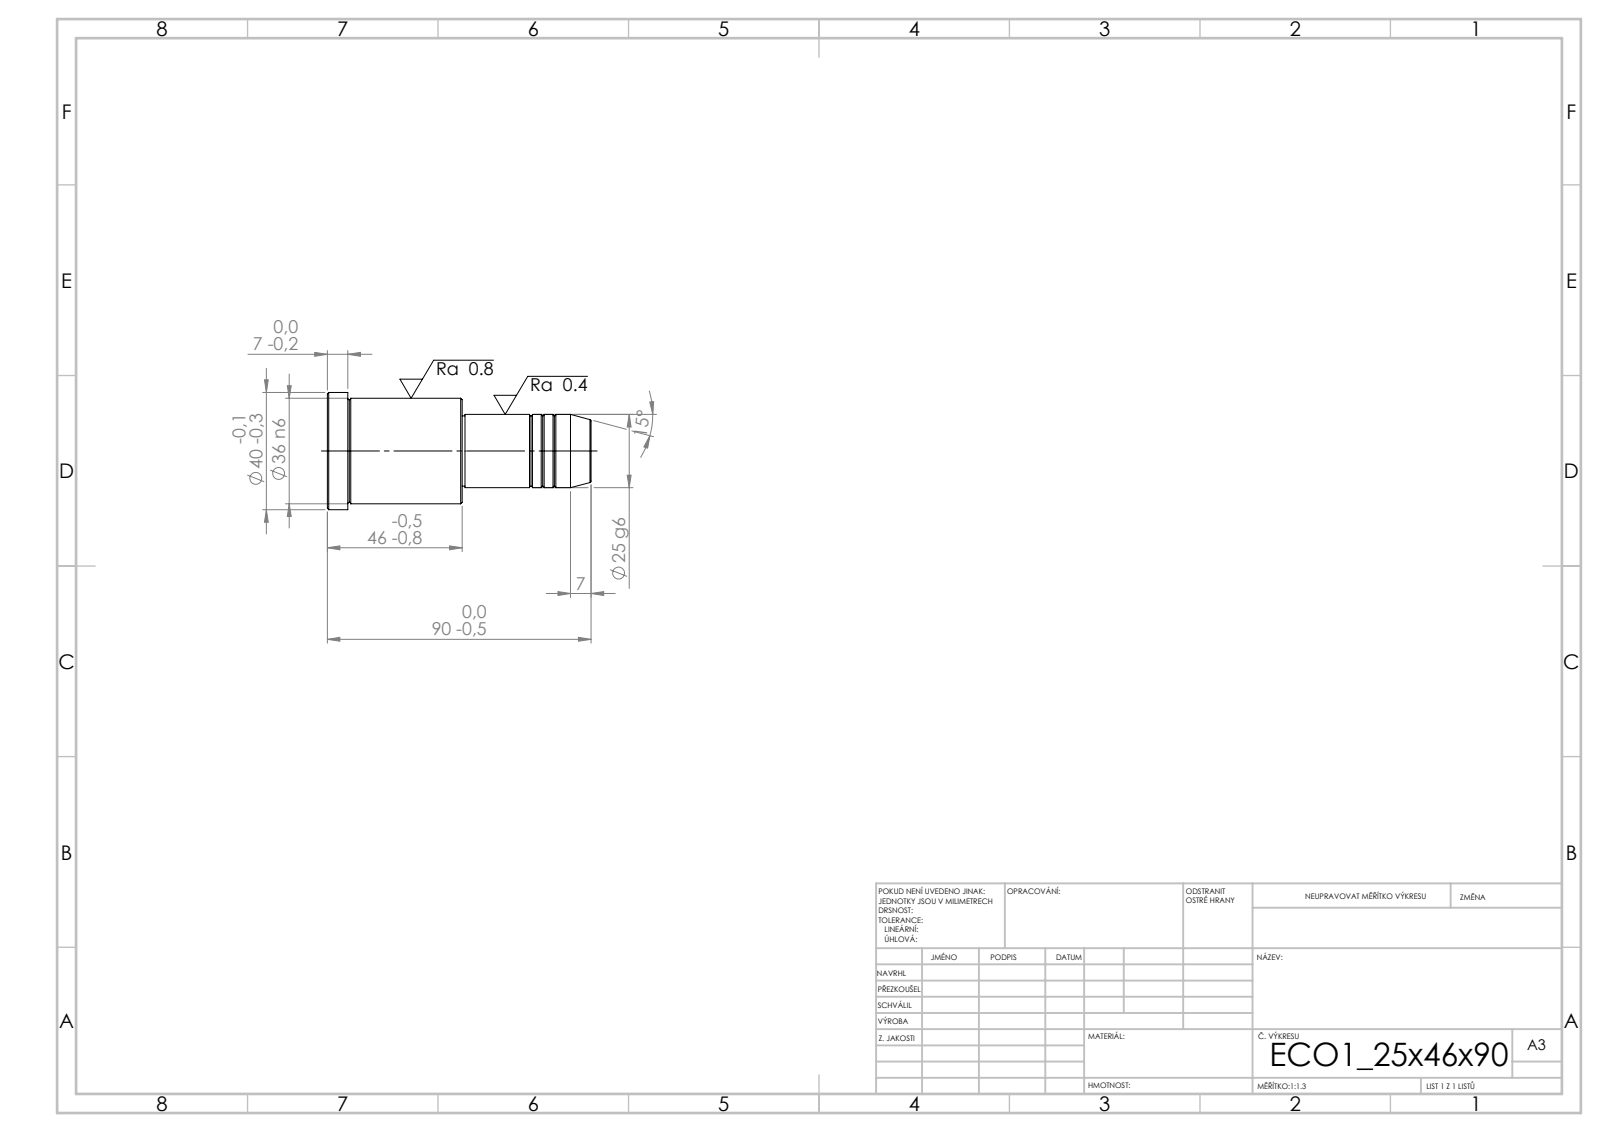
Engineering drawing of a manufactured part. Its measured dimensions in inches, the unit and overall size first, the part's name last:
Units: inches
Overall size (bounding box): 3.543 × 1.575 × 1.575
Round bosses / shafts (diameter × count): ⌀1.575 ×1, ⌀1.417 ×1, ⌀0.984 ×1, ⌀0.945 ×1
Main face-to-face distances: 1.811, 1.732, 3.543, 3.268, 1.535, 0.276, 1.693, 0.039, 1.575, 1.85
Volume: 4.235 in³ · Surface area: 17.49 in²
Bodies: 1 solid, 43 faces (5 planar, 14 cylindrical, 24 other)
STEP written by: SolidWorks 2019 (CONFIG_CONTROL_DESIGN)
